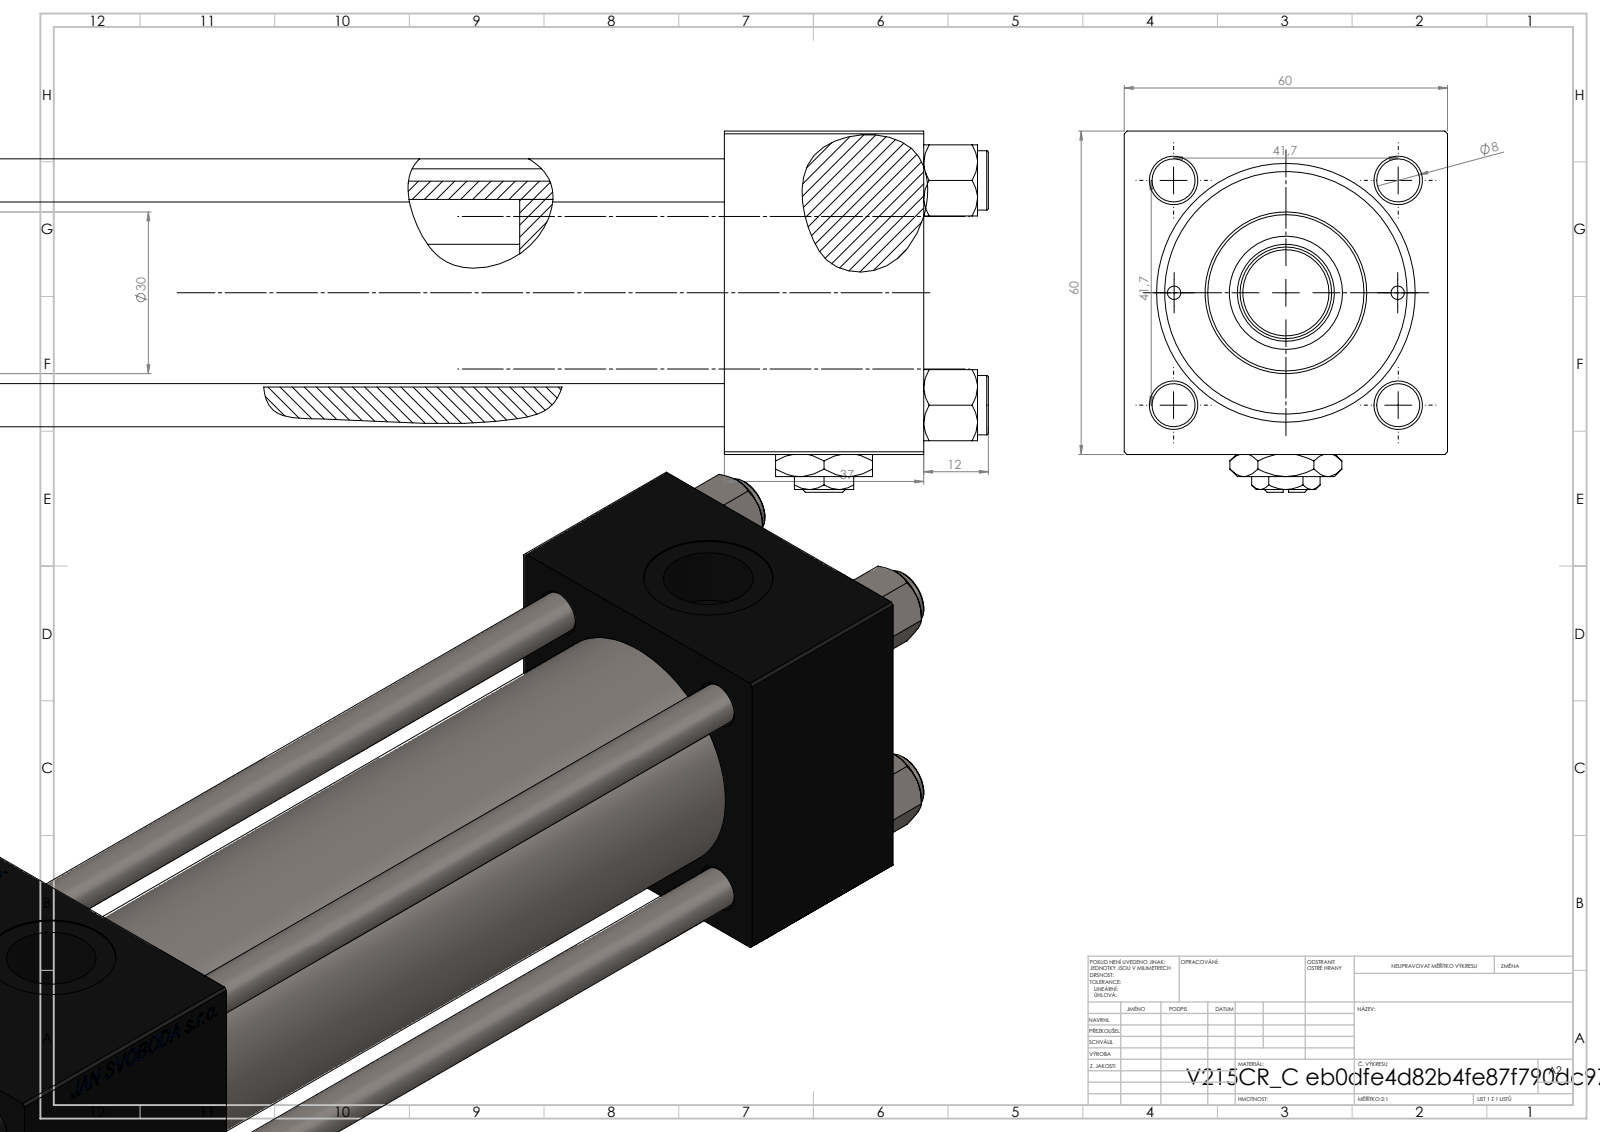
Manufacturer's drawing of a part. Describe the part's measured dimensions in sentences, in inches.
The part is named "V215CR_ROD_END_F; NUT_M5_C; V215CR_C_Body; V215CR_C_TYCINKA (+3 more)". Its 3-D file was written by "SolidWorks 2019 (CONFIG_CONTROL_DESIGN)". It is 14 solids with 1267 faces: 579 planar, 106 cylindrical and 582 other. Overall it measures 11.22 by 2.638 by 2.362 inches. Its volume is 28.73 cubic inches and its surface area 223.1 square inches. Round holes: 4 of diameter 0.315, 2 of diameter 0.098, 2 of diameter 0.276, 2 of diameter 0.656, 2 of diameter 0.945, 1 of diameter 0.335, 1 of diameter 0.709, 1 of diameter 0.827, 1 of diameter 1.22, 1 of diameter 1.575, 1 of diameter 1.772. Round bosses or shafts: 5 of diameter 0.433, 1 of diameter 1.811, 1 of diameter 1.181, 1 of diameter 0.669. The main face-to-face distances are 2.362, 1.457, 8.976, 7.52, 2.087, 6.89, 5.433, 7.846, 6.39, 0.957. The hole center spacings are 0.821, 1.161, 1.642, 1.832, 0.817, 2.322, 1.634, 6.791.
